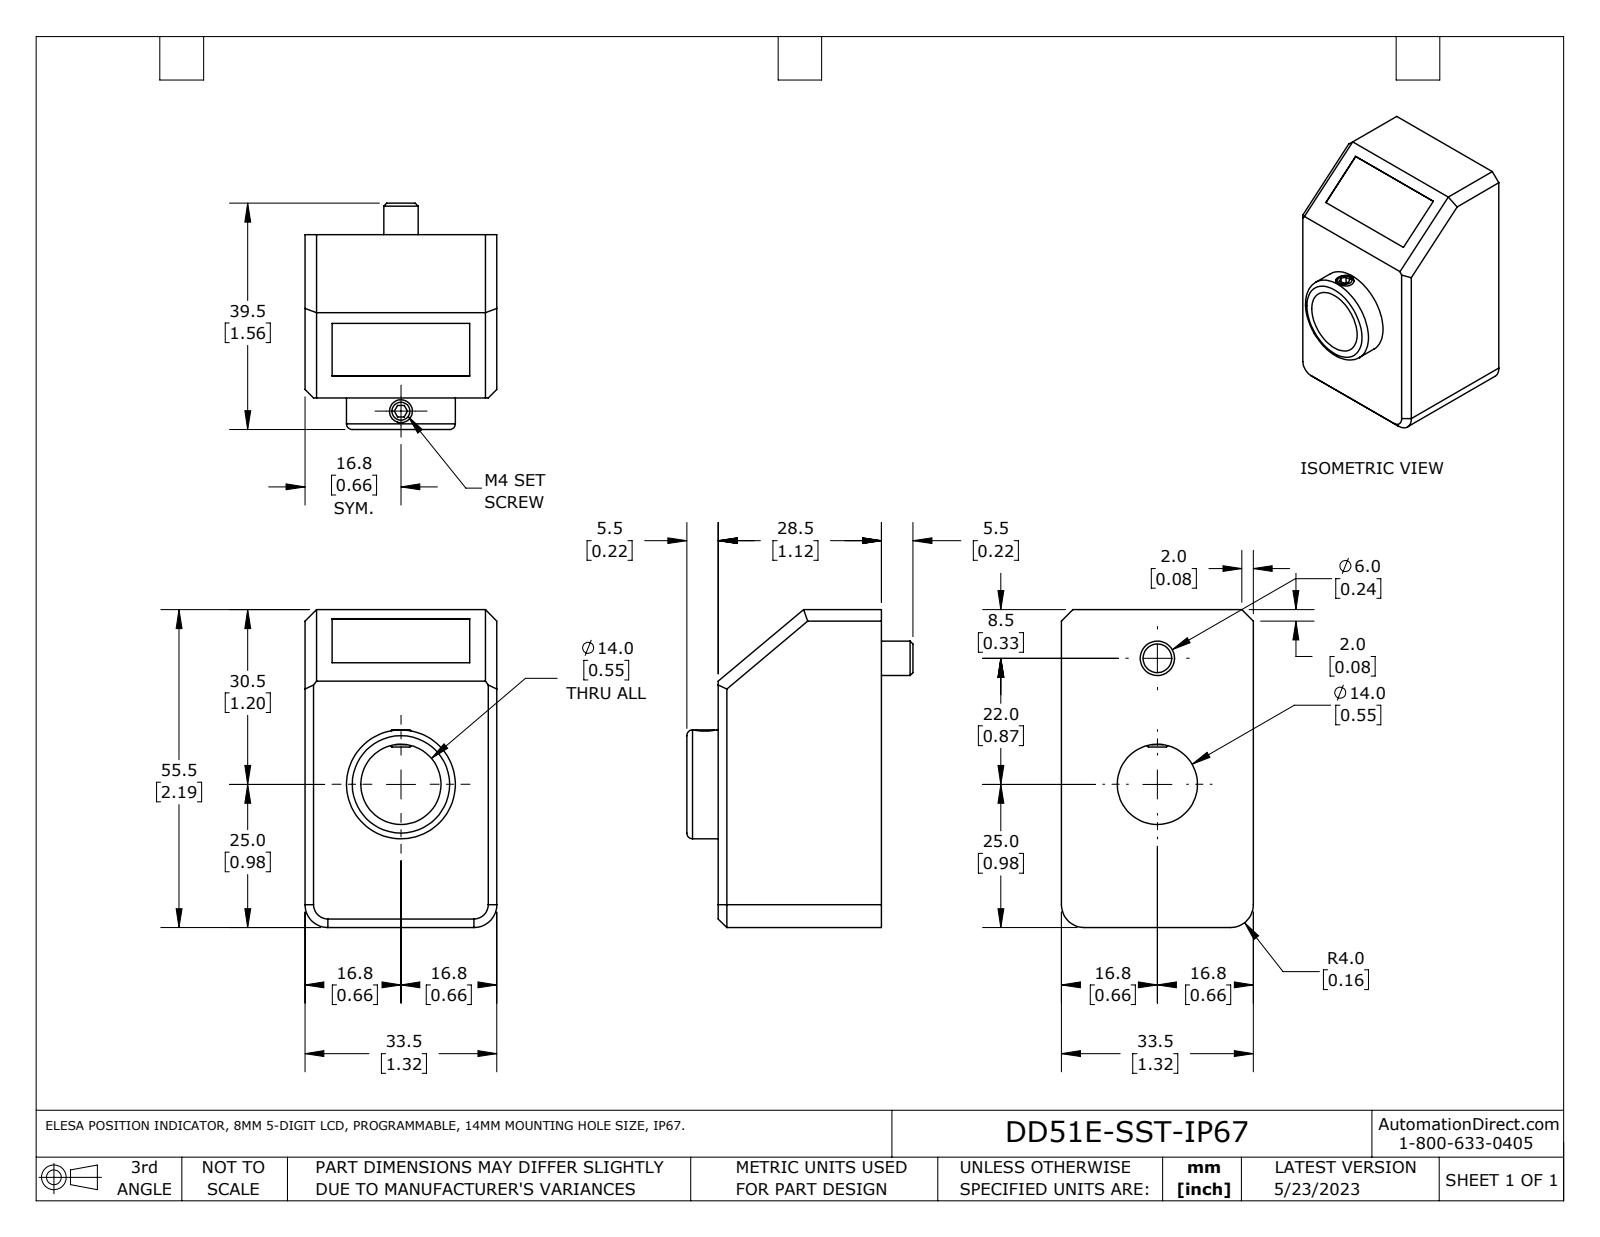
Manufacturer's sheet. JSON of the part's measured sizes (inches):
{"part_name": "DD51E-SST-IP67", "step_written_by": "SolidWorks 2021 (AUTOMOTIVE_DESIGN)", "units": "inches", "bodies": {"solids": 1, "faces": 46, "planar": 30, "cylindrical": 10, "other": 6}, "overall_size": [2.185, 1.555, 1.319], "volume_in3": 2.792, "surface_area_in2": 14.93, "round_holes": [[0.157, 1], [0.551, 1]], "round_bosses_or_shafts": [[0.748, 1], [0.236, 1]], "partial_cylinders_radius": [[0.157, 2]], "face_to_face_distances": [1.319, 1.122, 2.185, 0.217, 1.339, 1.555, 0.079, 0.945, 1.24, 1.358]}
